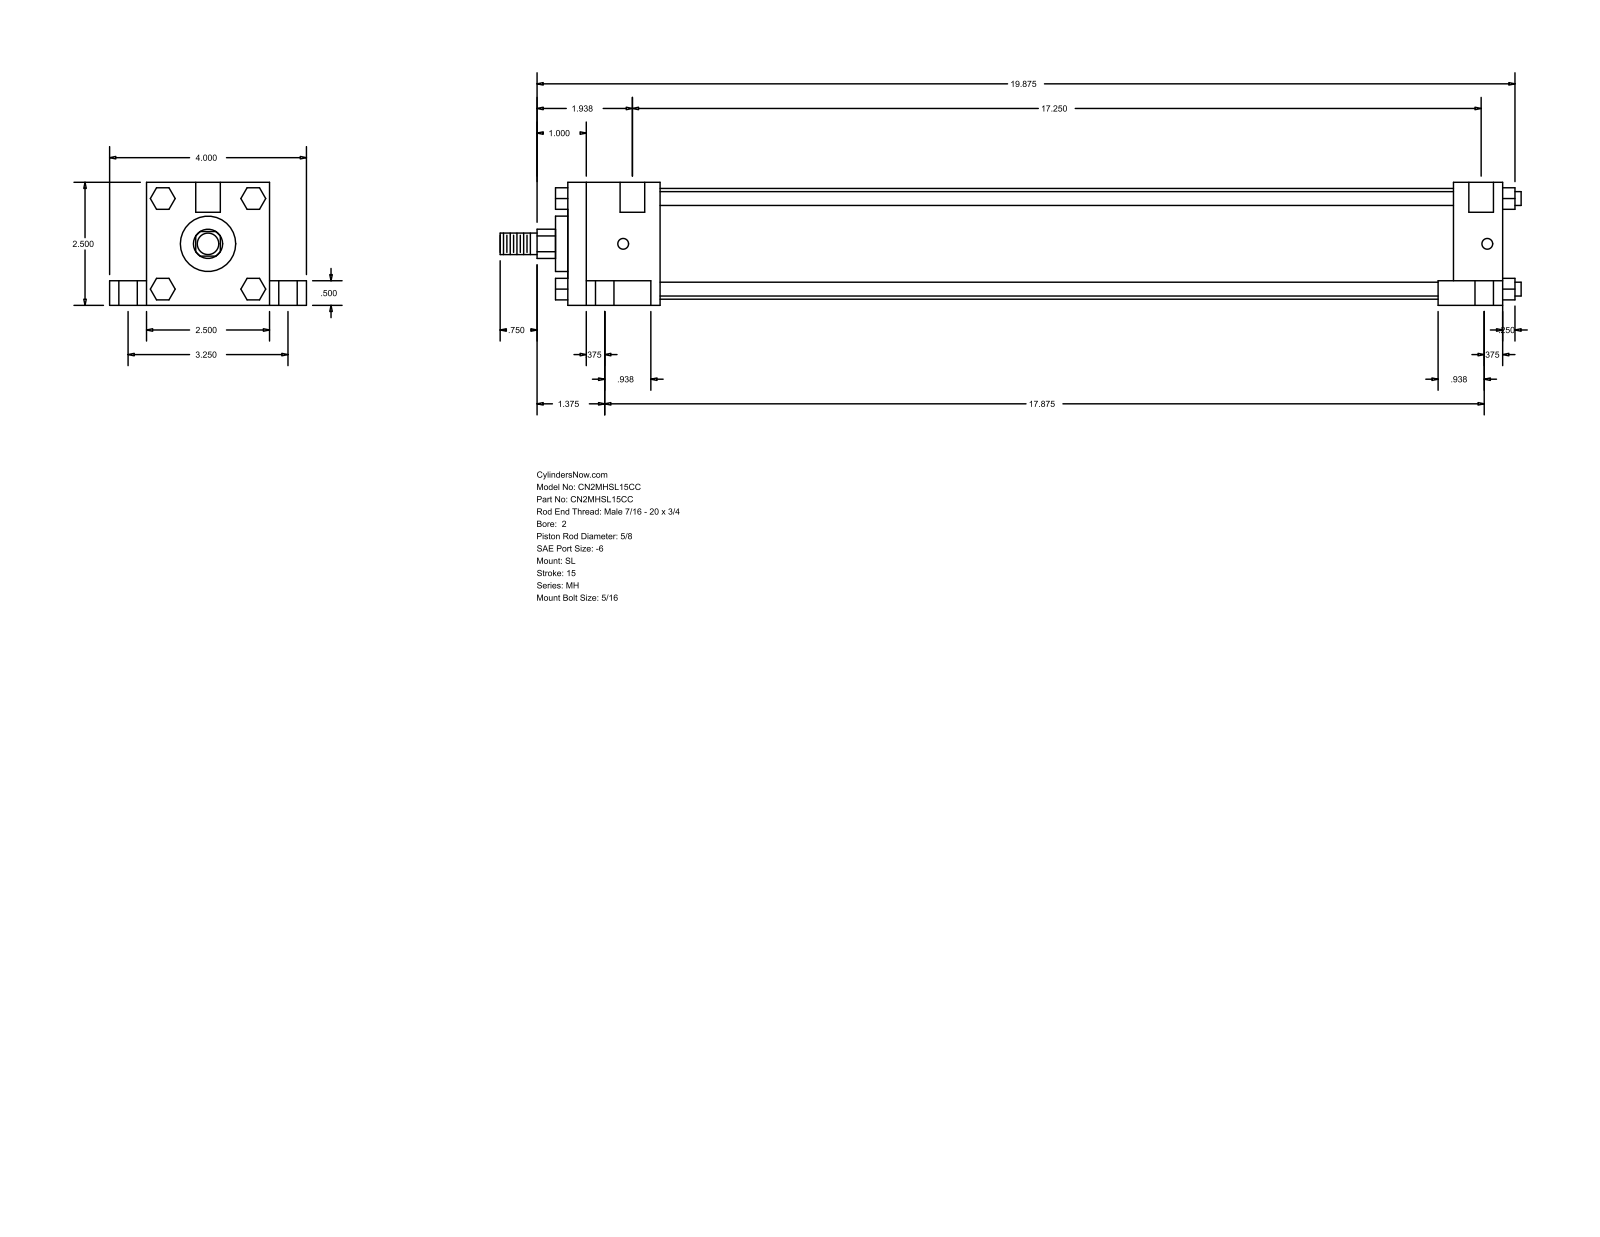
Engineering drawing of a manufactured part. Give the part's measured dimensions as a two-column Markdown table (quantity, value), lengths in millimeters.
| quantity | value |
| --- | --- |
| part name | MH_SL__0200_0.625 |
| STEP written by | GSSL Pune (CONFIG_CONTROL_DESIGN) |
| units | millimeters |
| bodies | 0 solids, 148 faces (112 planar, 36 cylindrical, 0 other) |
| overall size | 527.05 × 101.6 × 63.5 |
| round holes (diameter × count) | 5.56 × 4, 9.53 × 4, 15.88 × 4, 12.7 × 2 |
| round bosses / shafts (diameter × count) | 7.14 × 4, 57.15 × 1, 28.57 × 1, 15.88 × 1, 11.11 × 1 |
| partial cylindrical surfaces (radius × count) | 7.54 × 1 |
| main face-to-face distances | 63.5, 482.6, 12.7, 19.05, 82.55, 50.8, 457.19, 25.41, 47.62, 409.57 |
| hole center spacings | 41.3, 42.36, 43.67, 82.54, 441.67, 446.09, 446.41, 454.03 |
